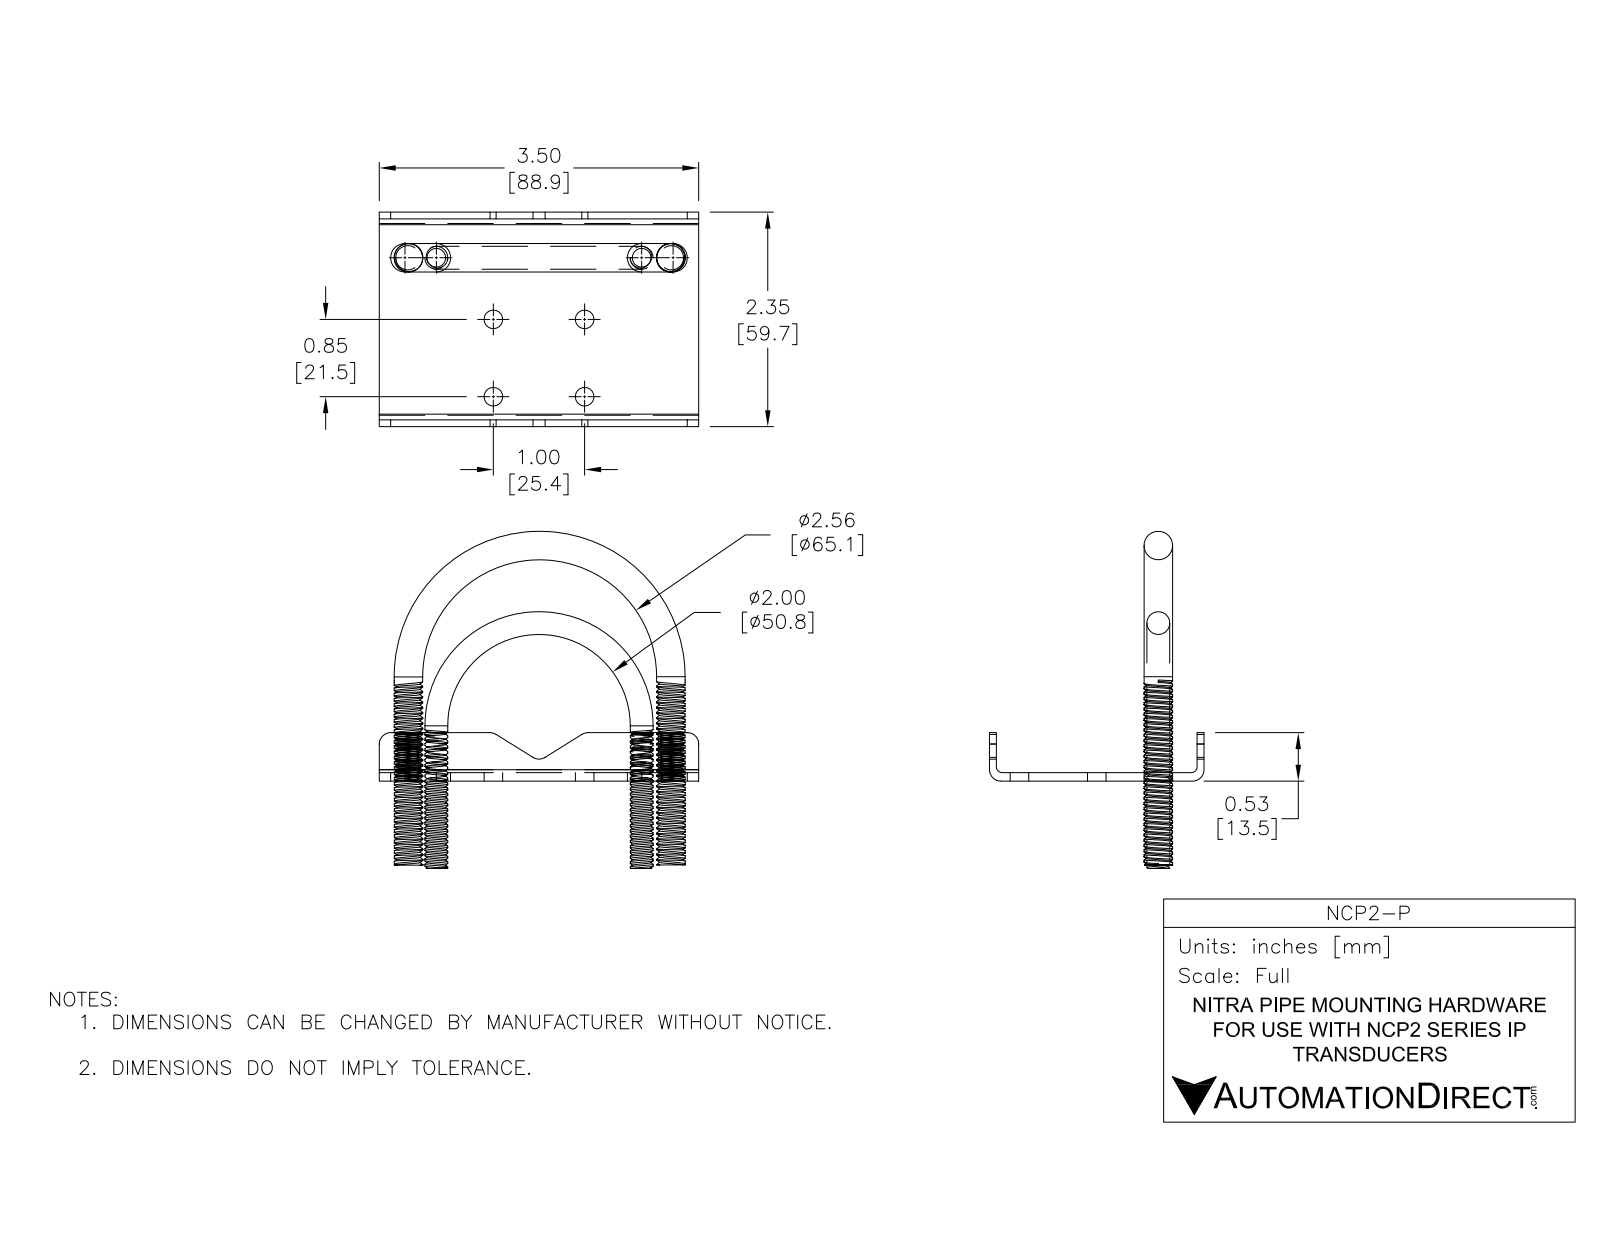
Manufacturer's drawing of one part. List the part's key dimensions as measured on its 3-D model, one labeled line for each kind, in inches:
Part name (STEP PRODUCT): NCP2-P
STEP written by: SolidWorks 2016 (AUTOMOTIVE_DESIGN)
Units: inches
Bodies: 3 solids, 322 faces (30 planar, 280 cylindrical, 12 other)
Overall size (bounding box): 3.693 × 3.5 × 2.35
Volume: 1.855 in³ · Surface area: 37.97 in²
Round holes (diameter × count): ⌀0.203 ×4
Round bosses / shafts (diameter × count): ⌀0.313 ×2, ⌀0.25 ×2
Partial cylindrical surfaces — rounded edges, fillets, slot ends (radius × count): R0.125 ×7, R0.156 ×4, R0.062 ×1, R0.063 ×1
Main face-to-face distances: 0.094, 2.35, 0.075, 2.275, 2.2, 2.275, 0.075, 0.531, 0.438, 3.5
Hole centre spacings: 0.847, 1, 1.31
